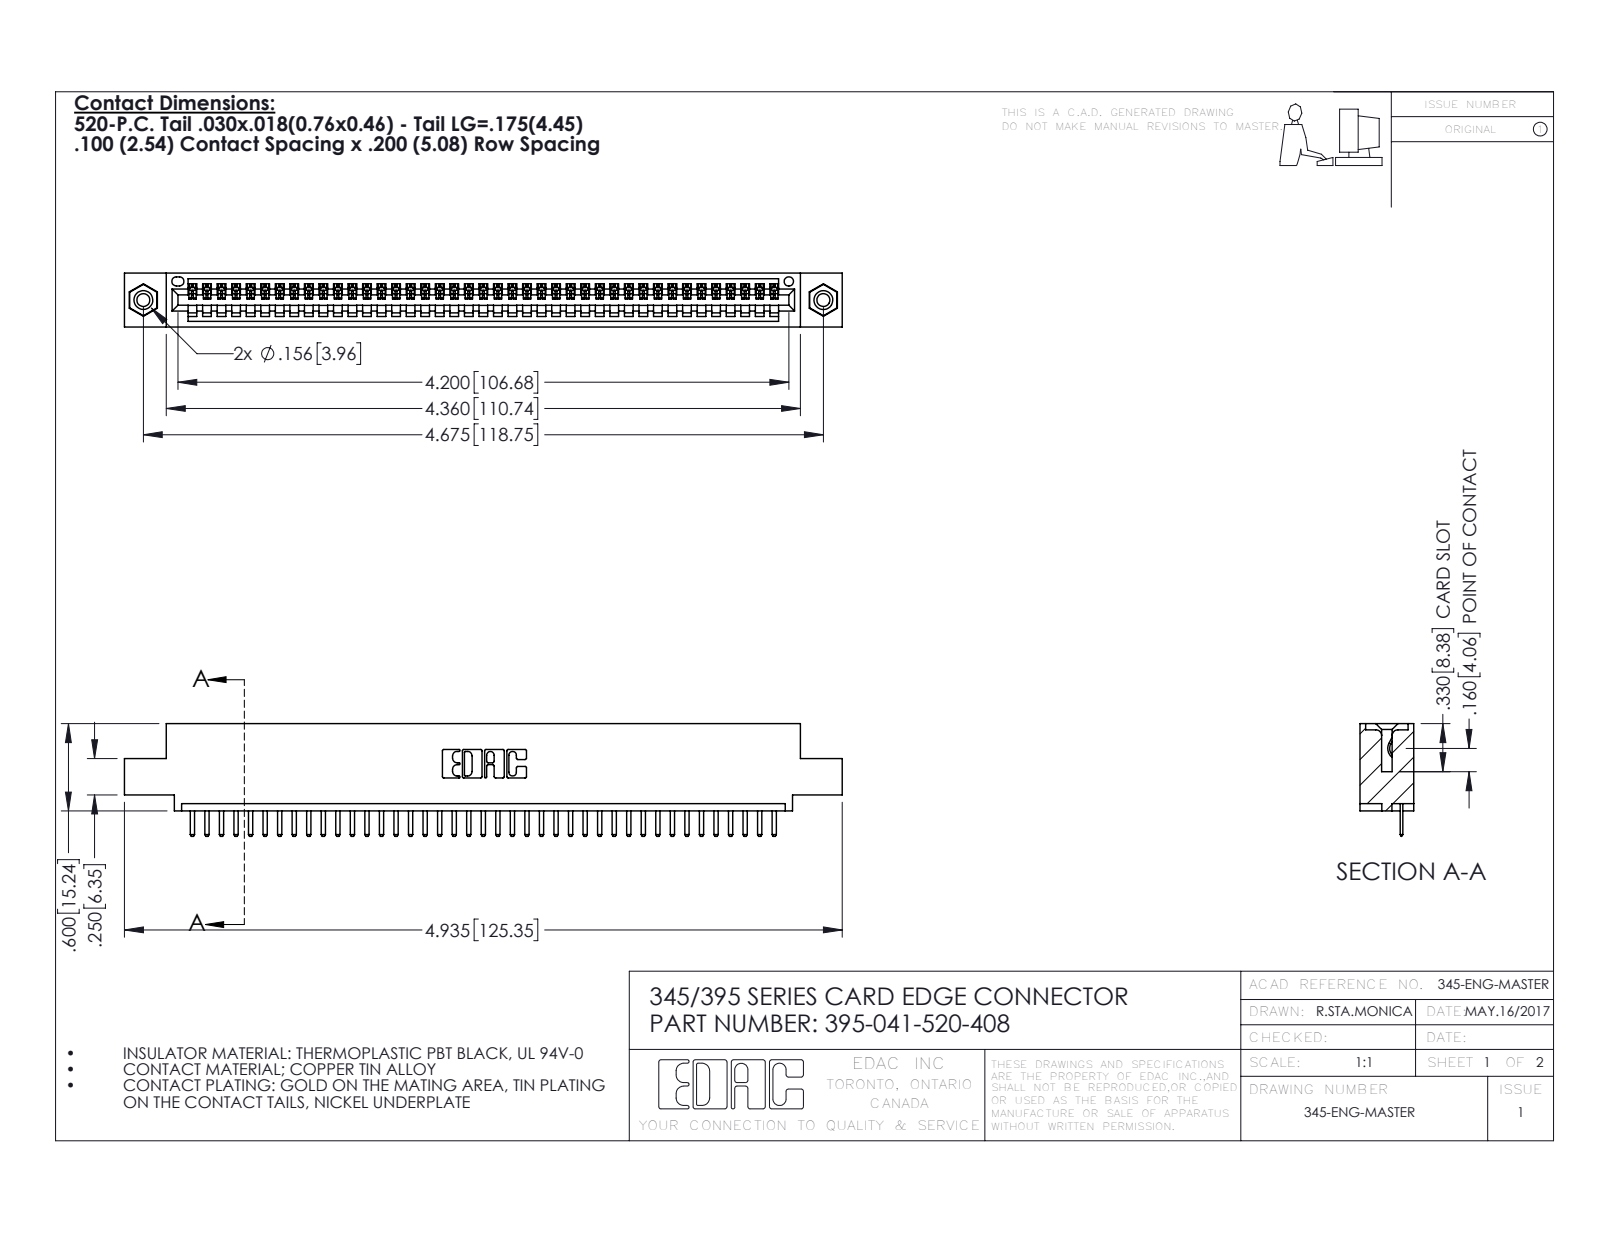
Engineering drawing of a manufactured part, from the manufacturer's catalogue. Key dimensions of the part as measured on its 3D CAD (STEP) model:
Part name (STEP PRODUCT): 345-292-001_345-293-120; 345 Part_0.110 Offset - 0.156 Dia-TI; 395-041-520-408; 345-250-001_345-250-003-102
STEP written by: SolidWorks 2016 (CONFIG_CONTROL_DESIGN)
Units: inches
Bodies: 44 solids, 2732 faces (1838 planar, 878 cylindrical, 16 other)
Overall size (bounding box): 4.935 × 0.775 × 0.37
Volume: 0.714 in³ · Surface area: 23.64 in²
Round holes (diameter × count): ⌀0.089 ×2, ⌀0.125 ×2, ⌀0.156 ×2, ⌀0.064 ×1
Round bosses / shafts (diameter × count): ⌀0.155 ×2
Partial cylindrical surfaces — rounded edges, fillets, slot ends (radius × count): R0.01 ×84, R0.006 ×82, R0.01 ×22, R0.007 ×6, R0.031 ×6, R0.026 ×3, R0.031 ×2, R0.04 ×2
Main face-to-face distances: 0.072, 0.298, 0.37, 0.2, 0.098, 0.272, 0.025, 0.225, 0.072, 0.149
Hole centre spacings: 0.27, 4.439, 4.675
